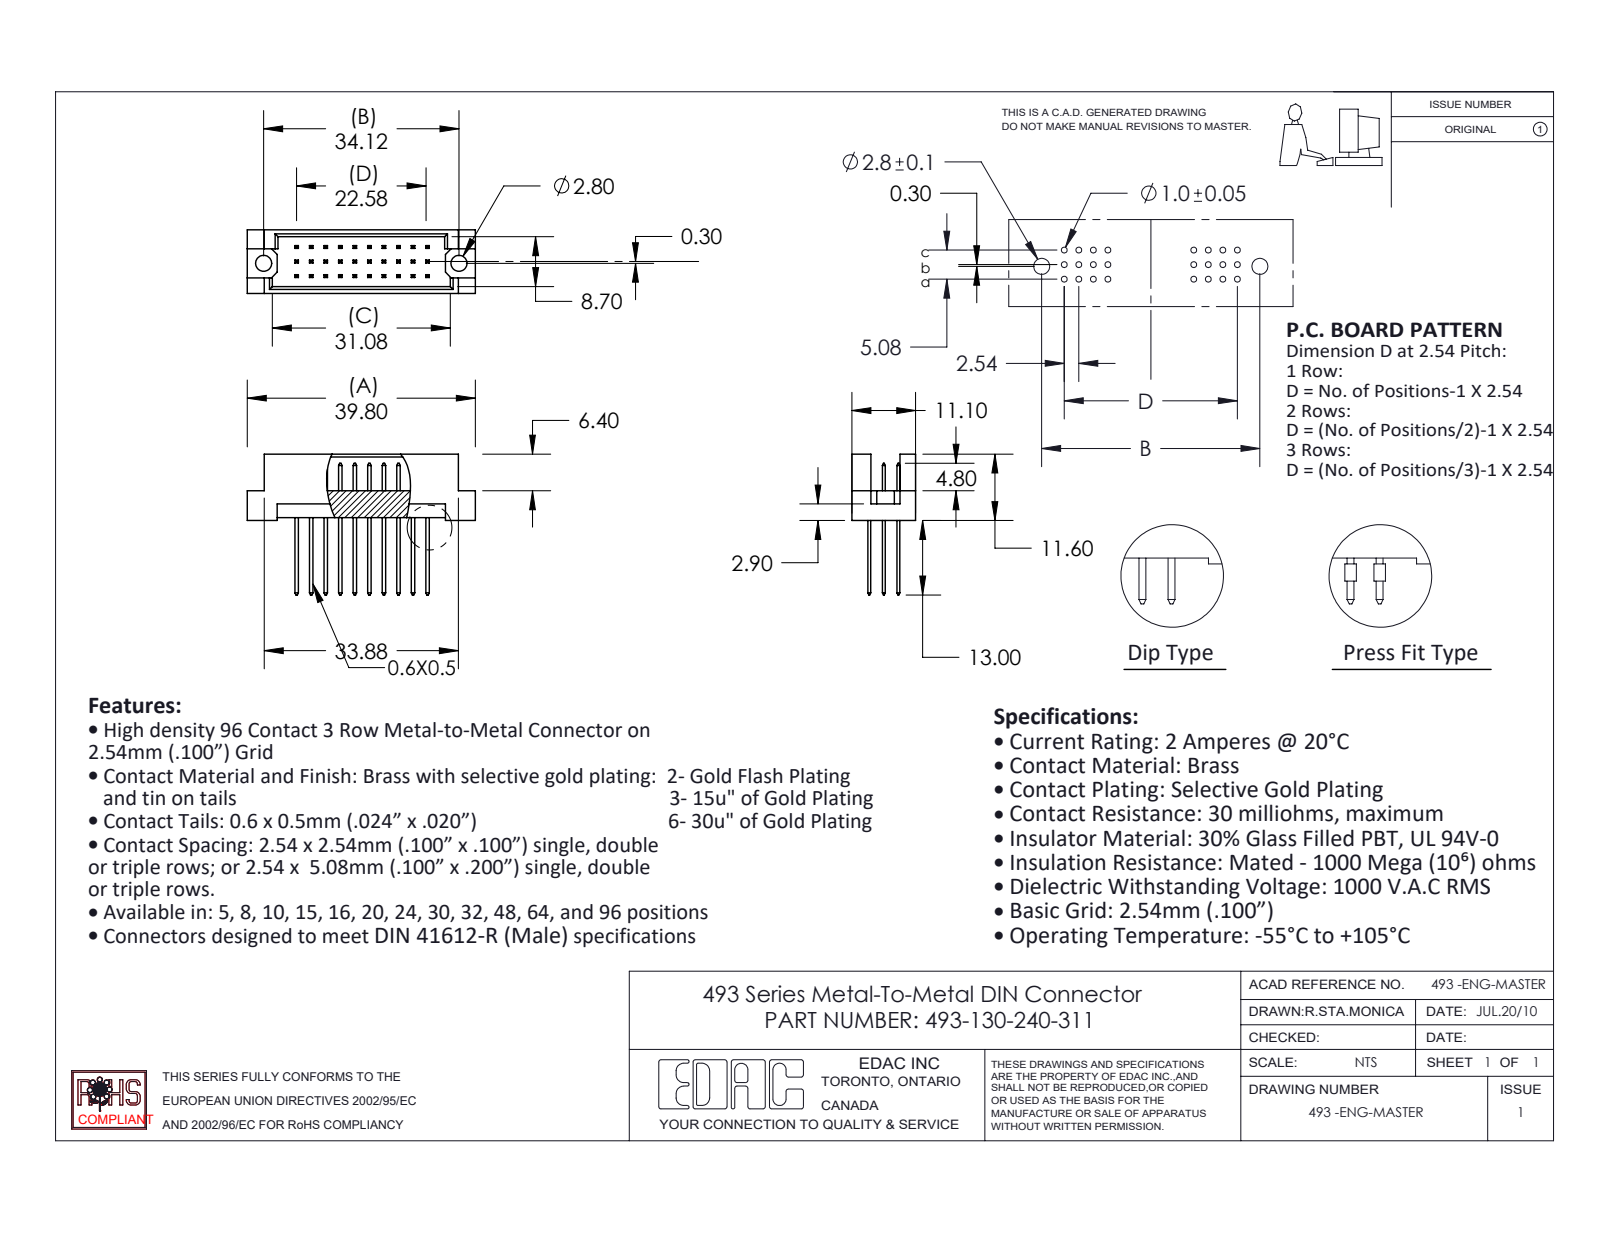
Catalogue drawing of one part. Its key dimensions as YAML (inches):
part_name: "493-130-240-311; 493 Part_30; 493-290_40"
step_written_by: "SolidWorks 2020 (CONFIG_CONTROL_DESIGN)"
units: inches
bodies: {solids: 31, faces: 592, planar: 588, cylindrical: 4, other: 0}
overall_size: [1.567, 0.969, 0.437]
volume: 0.157
surface_area: 6.578
round_holes:
  - {diameter: 0.11, count: 2}
face_to_face_distances: [0.1, 0.2, 0.02, 0.047, 0.39, 0.3, 0.4, 0.437, 0.076, 0.5]
hole_center_spacings: [1.343]
